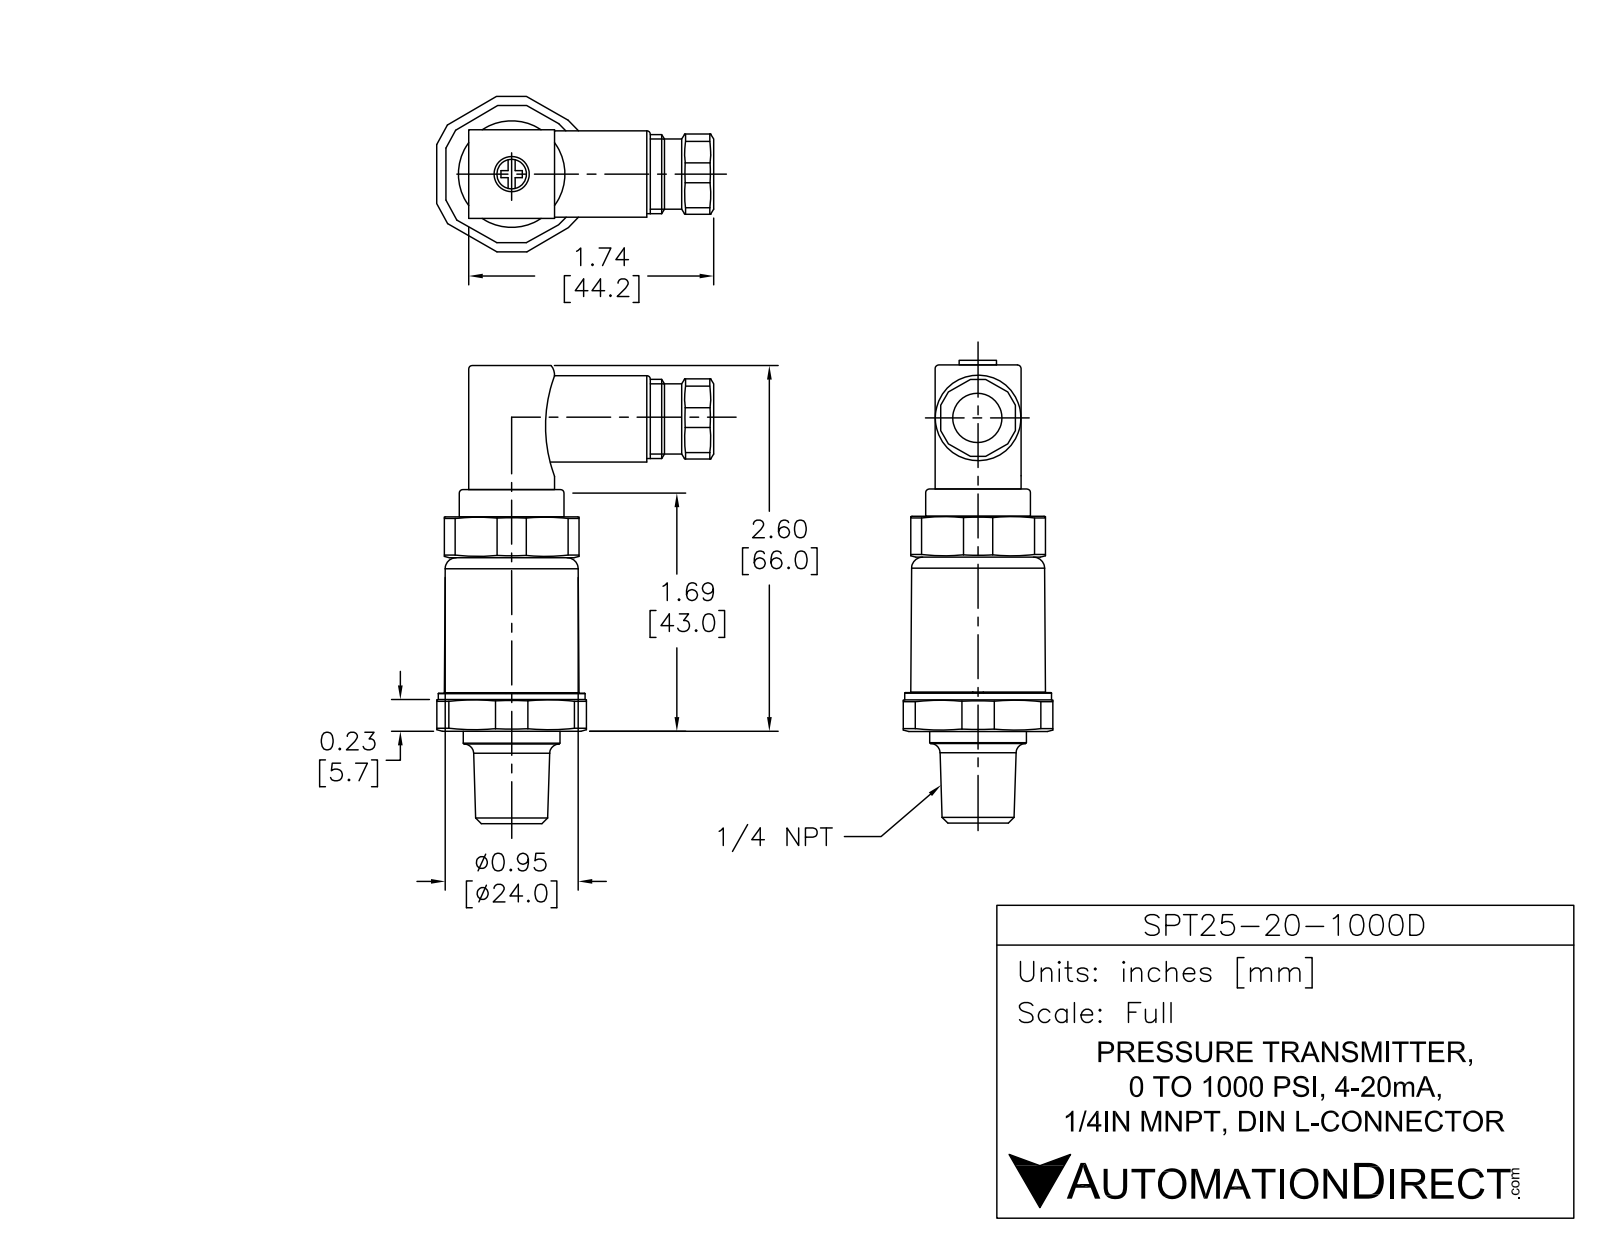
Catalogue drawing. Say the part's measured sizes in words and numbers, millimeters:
The part is named "SPT25-20-1000D". Its 3-D file was written by "SolidWorks 2011 (AUTOMOTIVE_DESIGN)". It is 5 solids with 170 faces: 96 planar, 64 cylindrical and 10 other. Overall it measures 81.25 by 38.01 by 35.71 millimeters. Its volume is 27 900 cubic millimeters and its surface area 10 134 square millimeters. Round holes: 1 of diameter 1, 1 of diameter 3.3, 1 of diameter 7, 1 of diameter 8. Round bosses or shafts: 1 of diameter 26.75, 1 of diameter 24, 1 of diameter 17.5, 1 of diameter 15, 1 of diameter 14, 1 of diameter 11. Partial cylindrical surfaces (rounded edges, fillets, slot ends): 8 of radius 1.5, 4 of radius 1.15, 4 of radius 2.25, 3 of radius 2, 1 of radius 1.15, 1 of radius 1.17, 1 of radius 14.5. The main face-to-face distances are 1.5, 29.5, 31, 15.75, 0.35, 15.4, 6.75, 37.75, 36.25, 5. The hole center spacings are 1.33.
